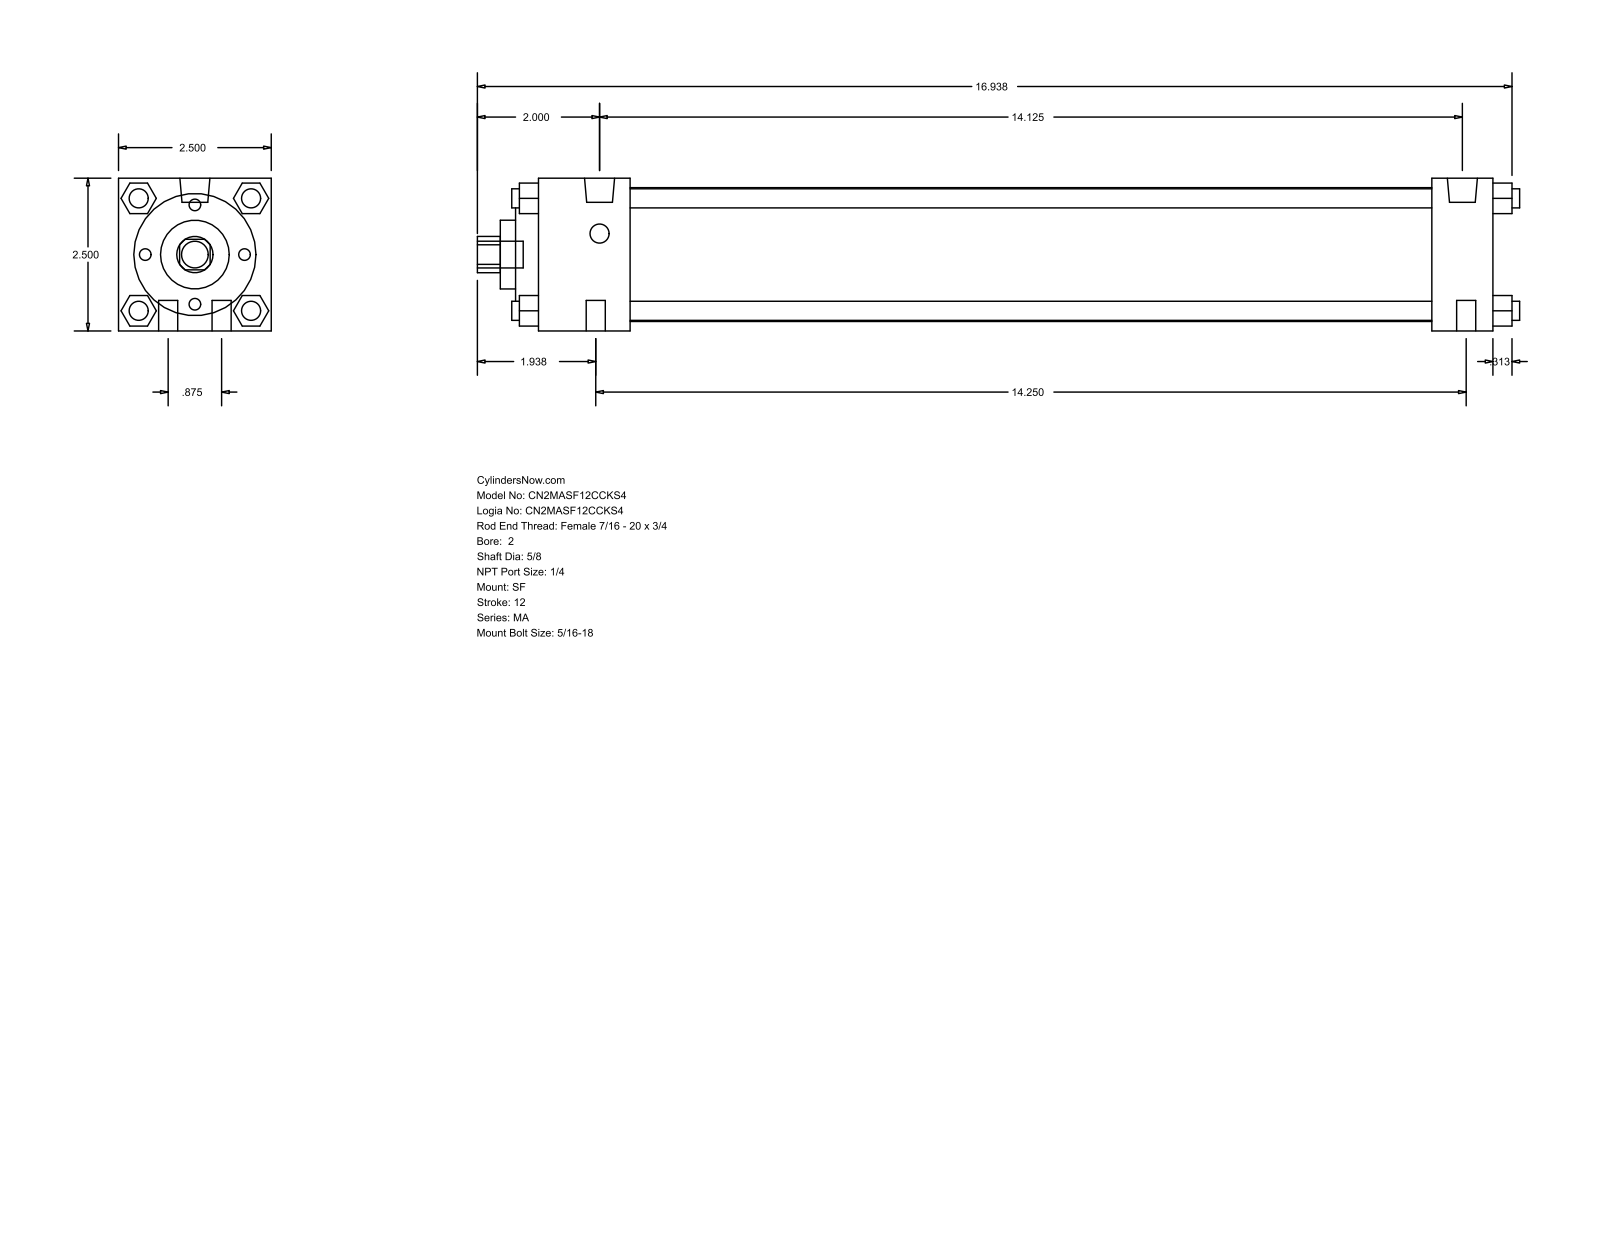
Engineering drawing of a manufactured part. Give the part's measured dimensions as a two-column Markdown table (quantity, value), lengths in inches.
| quantity | value |
| --- | --- |
| part name | MA_SF__0200_0.625 |
| STEP written by | GSSL Pune (CONFIG_CONTROL_DESIGN) |
| units | inches |
| bodies | 0 solids, 126 faces (95 planar, 31 cylindrical, 0 other) |
| overall size | 17.063 × 2.5 × 2.5 |
| round holes (diameter × count) | 0.625 × 1, 1.125 × 1, 2 × 1, 2.19 × 1 |
| round bosses / shafts (diameter × count) | 0.313 × 10, 0.492 × 2, 0.437 × 1 |
| partial cylindrical surfaces (radius × count) | 0.297 × 1 |
| main face-to-face distances | 2.5, 0.5, 1.5, 0.375, 15.625, 14.625, 1, 13.125, 14.125, 1.875 |
